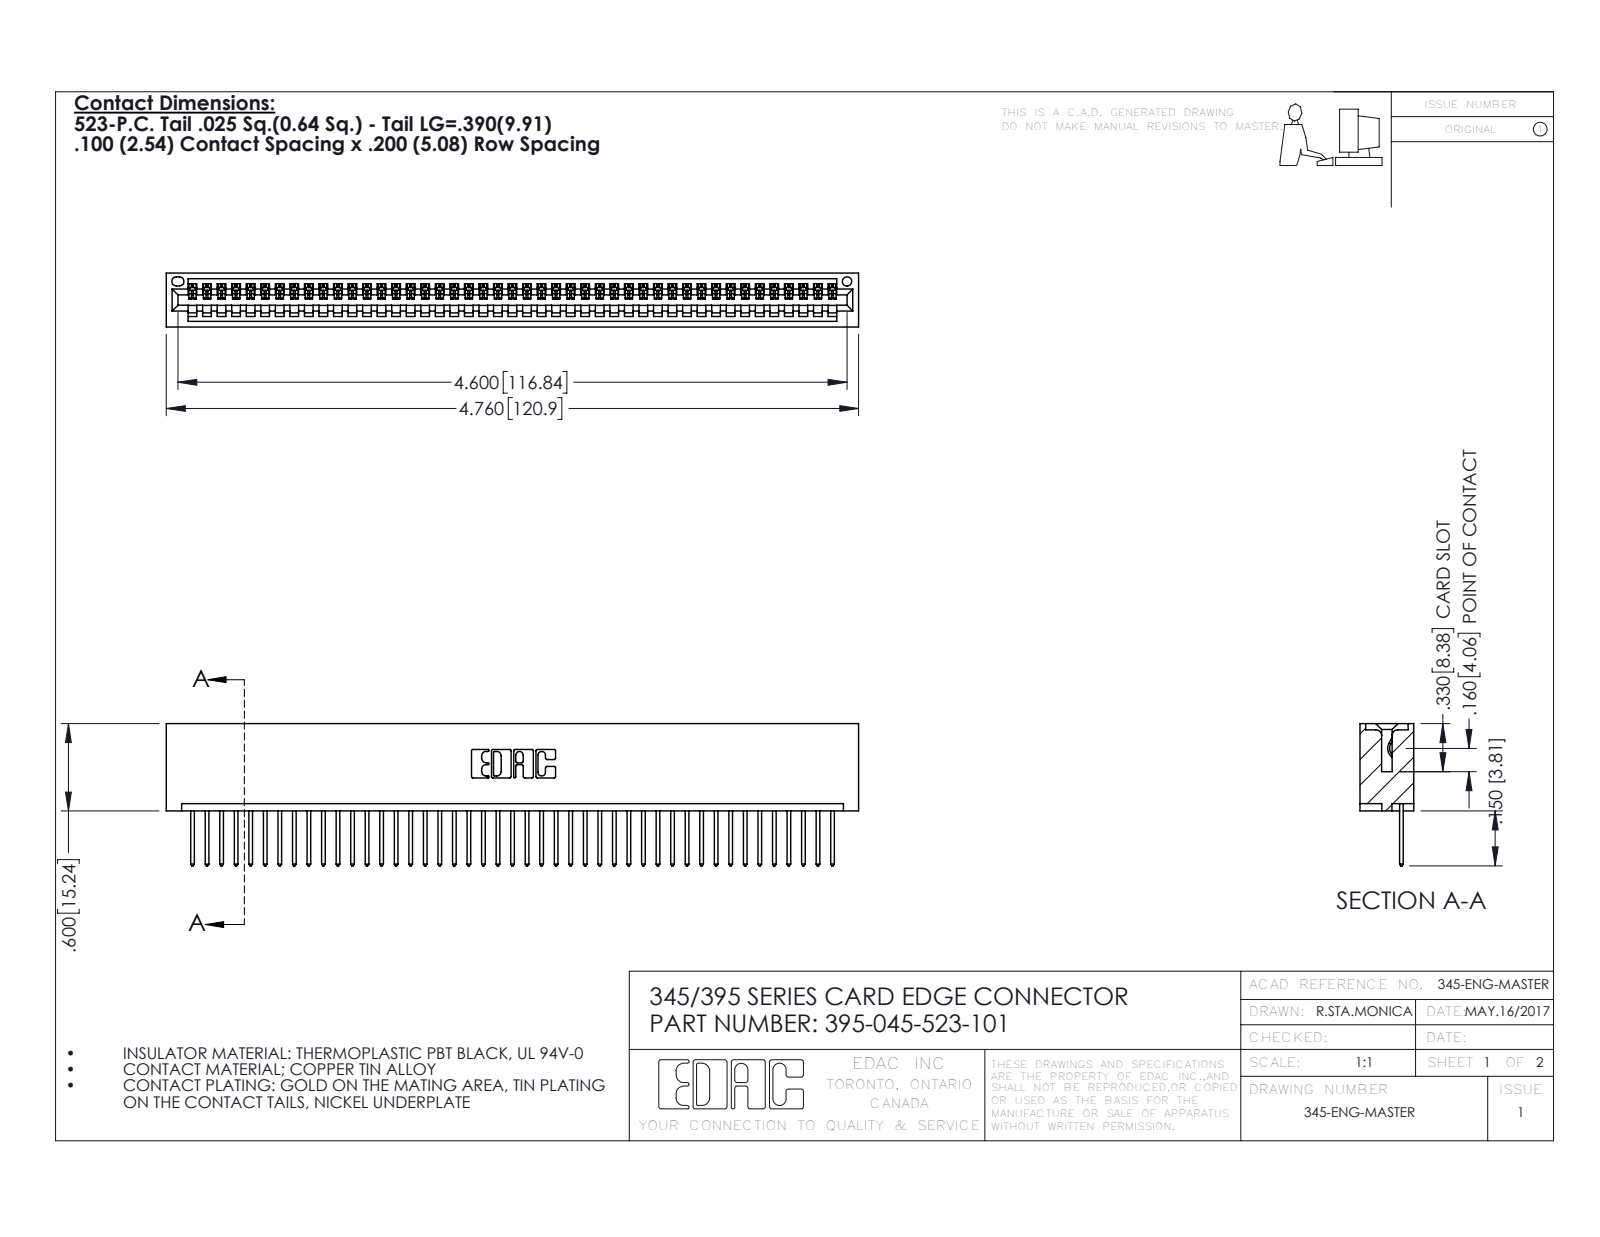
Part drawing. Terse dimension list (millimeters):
name: 345-292-001_345-293-123; 395-045-523-101; 345 Part_No Mounting Lugs
written by: SolidWorks 2016 (CONFIG_CONTROL_DESIGN)
unit: mm
bodies: 46 solids, 2728 faces (1876 planar, 852 cylindrical, 0 other)
size: 120.9 × 24.8 × 9.4
volume: 12 100 mm³; area: 16 330 mm²
holes: 1× ⌀1.6
rounds: 90× R0.2, 90× R0.3, 22× R0.3, 6× R0.2, 6× R0.8, 3× R0.7, 2× R0.8, 2× R1
face distances: 7.6, 1.8, 9.4, 5.1, 2.5, 6.9, 0.6, 5.7, 3.8, 1.8
